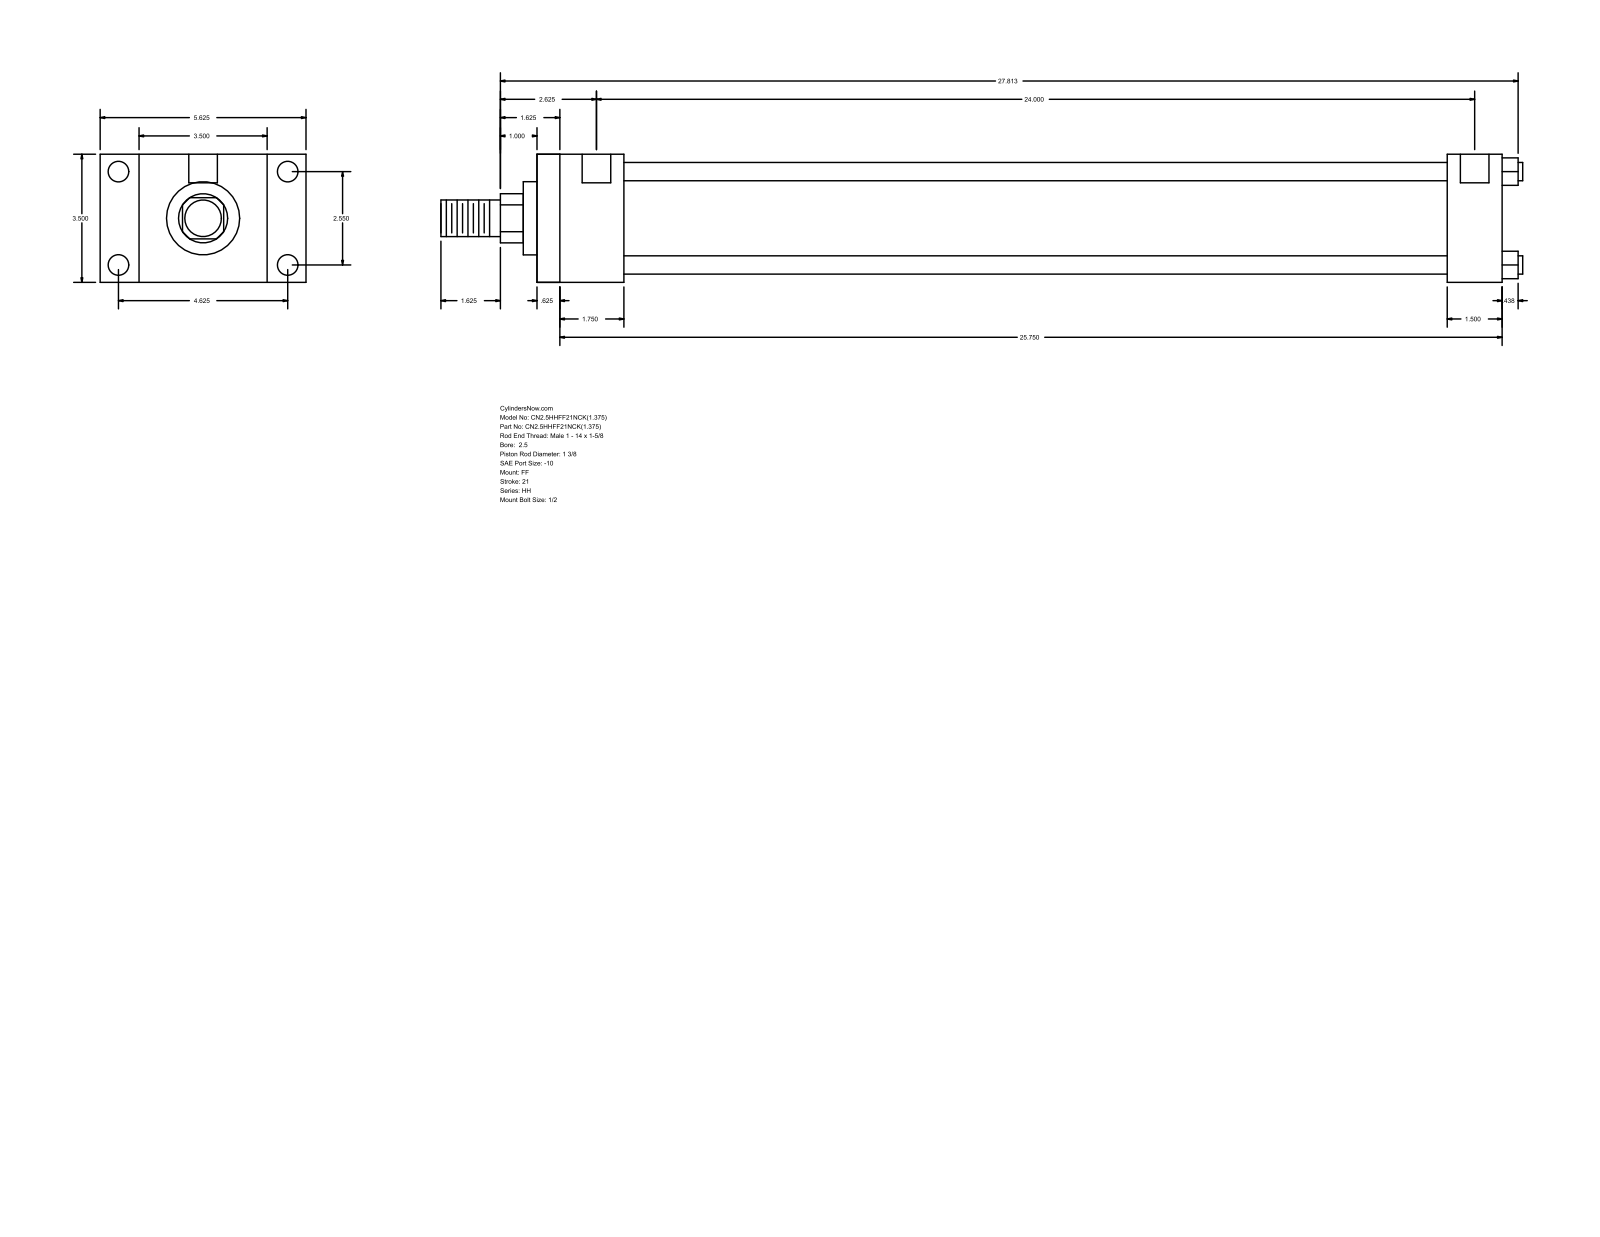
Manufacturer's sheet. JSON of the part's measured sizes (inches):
{"part_name": "HH_FF__0250_1.375", "step_written_by": "GSSL Pune (CONFIG_CONTROL_DESIGN)", "units": "inches", "bodies": {"solids": 0, "faces": 92, "planar": 64, "cylindrical": 28, "other": 0}, "overall_size": [29.563, 5.625, 3.5], "round_holes": [[0.219, 4], [0.563, 4], [0.781, 2]], "round_bosses_or_shafts": [[0.5, 4], [2.875, 1], [2, 1], [1.375, 1], [1, 1]], "partial_cylinders_radius": [[0.672, 1]], "face_to_face_distances": [3.5, 26.375, 0.625, 25.75, 2.375, 1.75, 24, 24.875, 24.25, 22.5], "hole_center_spacings": [2.55, 4.625, 5.281, 24.125, 0.062, 0.063, 24, 24.062]}
